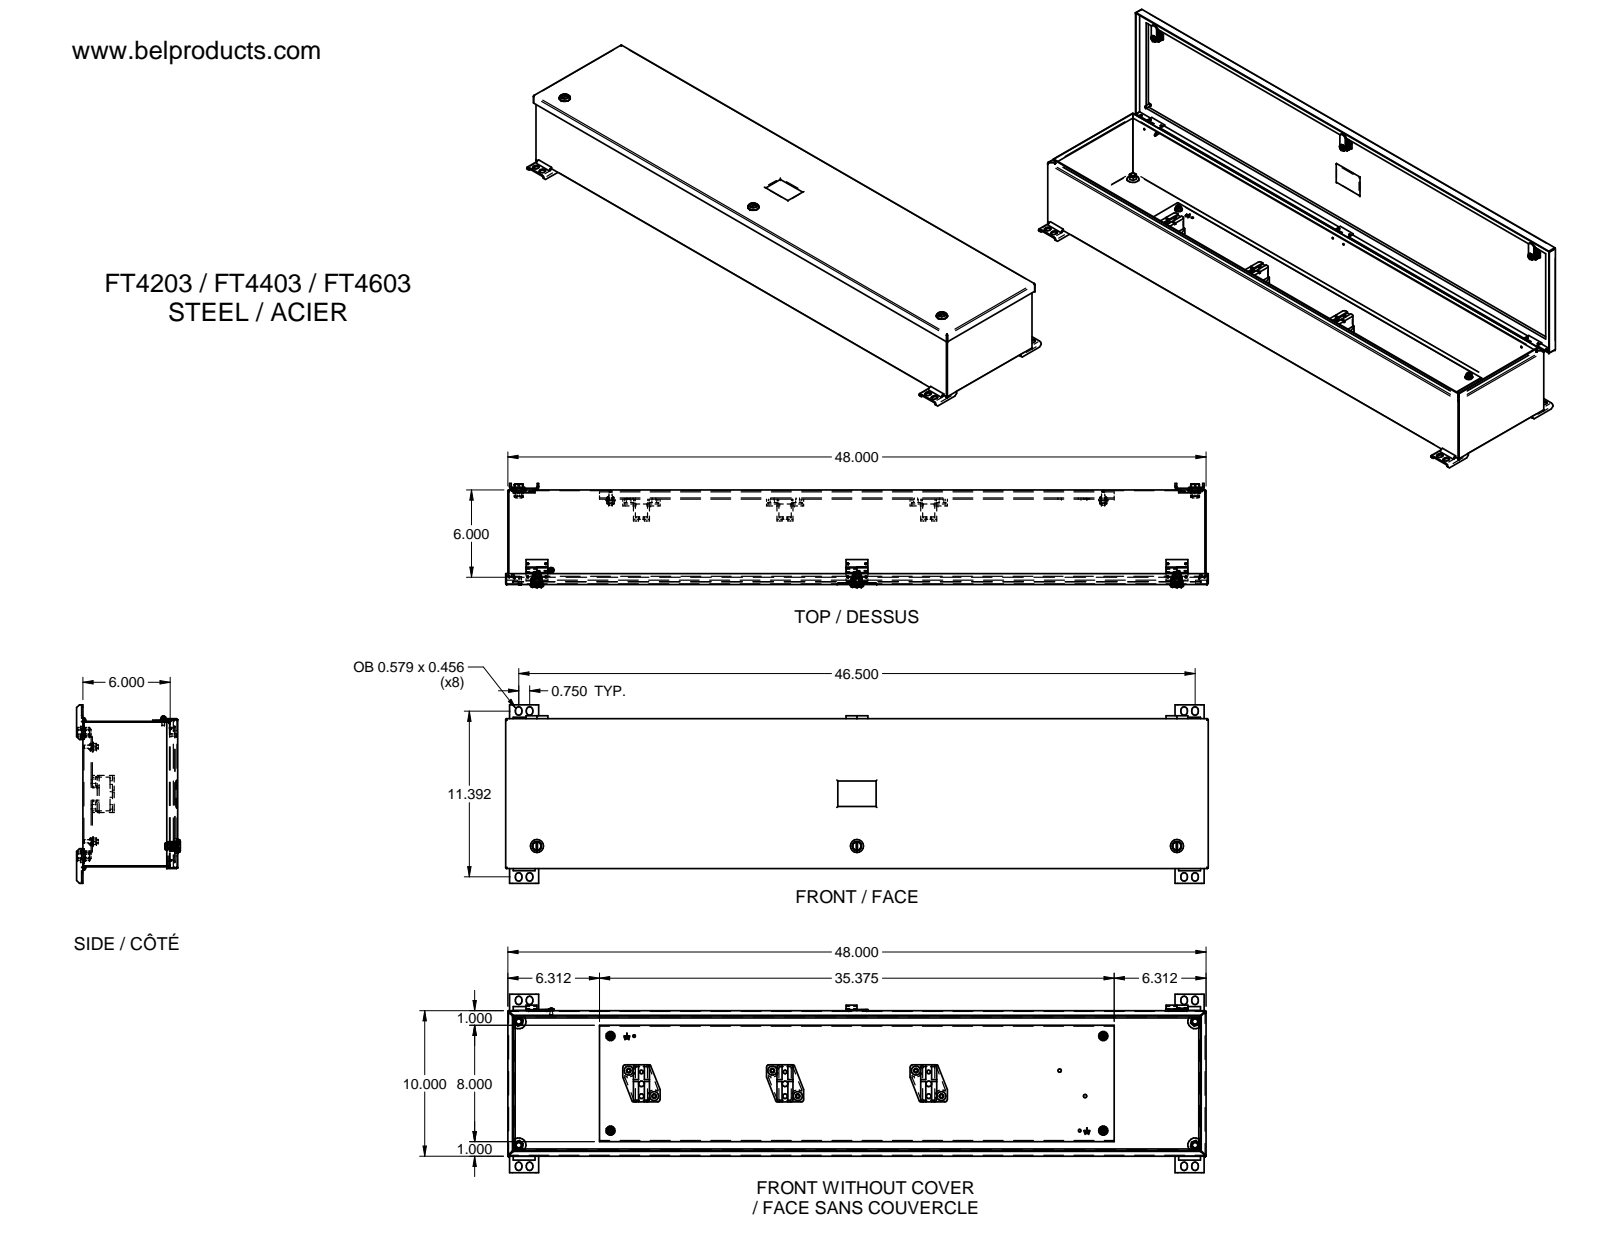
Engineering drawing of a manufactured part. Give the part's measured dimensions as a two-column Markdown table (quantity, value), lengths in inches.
| quantity | value |
| --- | --- |
| part name | LOCK AVEC TOURNEVIS TYPE 4-12 SANS CAME-oa8; HOSING-oa0; INSERT POUR TOURNEVIS-oa1; NOIX DE FIXATION-oa2 (+8 more) |
| STEP written by | Unknown (AUTOMOTIVE_DESIGN) |
| units | inches |
| bodies | 79 solids, 2953 faces (1705 planar, 587 cylindrical, 661 other) |
| overall size | 48.3 × 12.266 × 7.125 |
| volume | 166.2 in³ |
| surface area | 4 757 in² |
| round holes (diameter × count) | 0.124 × 12, 0.13 × 12, 0.236 × 8, 0.375 × 8, 0.456 × 8, 0.25 × 7, 0.312 × 6, 0.625 × 6, 0.125 × 5, 0.281 × 4, 0.355 × 4, 0.406 × 4 |
| round bosses / shafts (diameter × count) | 0.125 × 12, 0.119 × 5, 0.812 × 4, 0.625 × 4, 0.219 × 4, 0.031 × 4, 0.9 × 3, 0.89 × 3 |
| partial cylindrical surfaces (radius × count) | 0.375 × 32, 0.01 × 24, 0.187 × 22, 0.032 × 18, 0.092 × 16, 0.228 × 16, 0.057 × 12, 0.06 × 8 |
| main face-to-face distances | 0.06, 9.94, 0.06, 6.454, 6.514, 6.394, 6.454, 0.075, 0.641, 0.581 |
| hole center spacings | 9.875, 19.75, 9.875, 0.907, 22, 1.25, 2.475, 8.311 |
